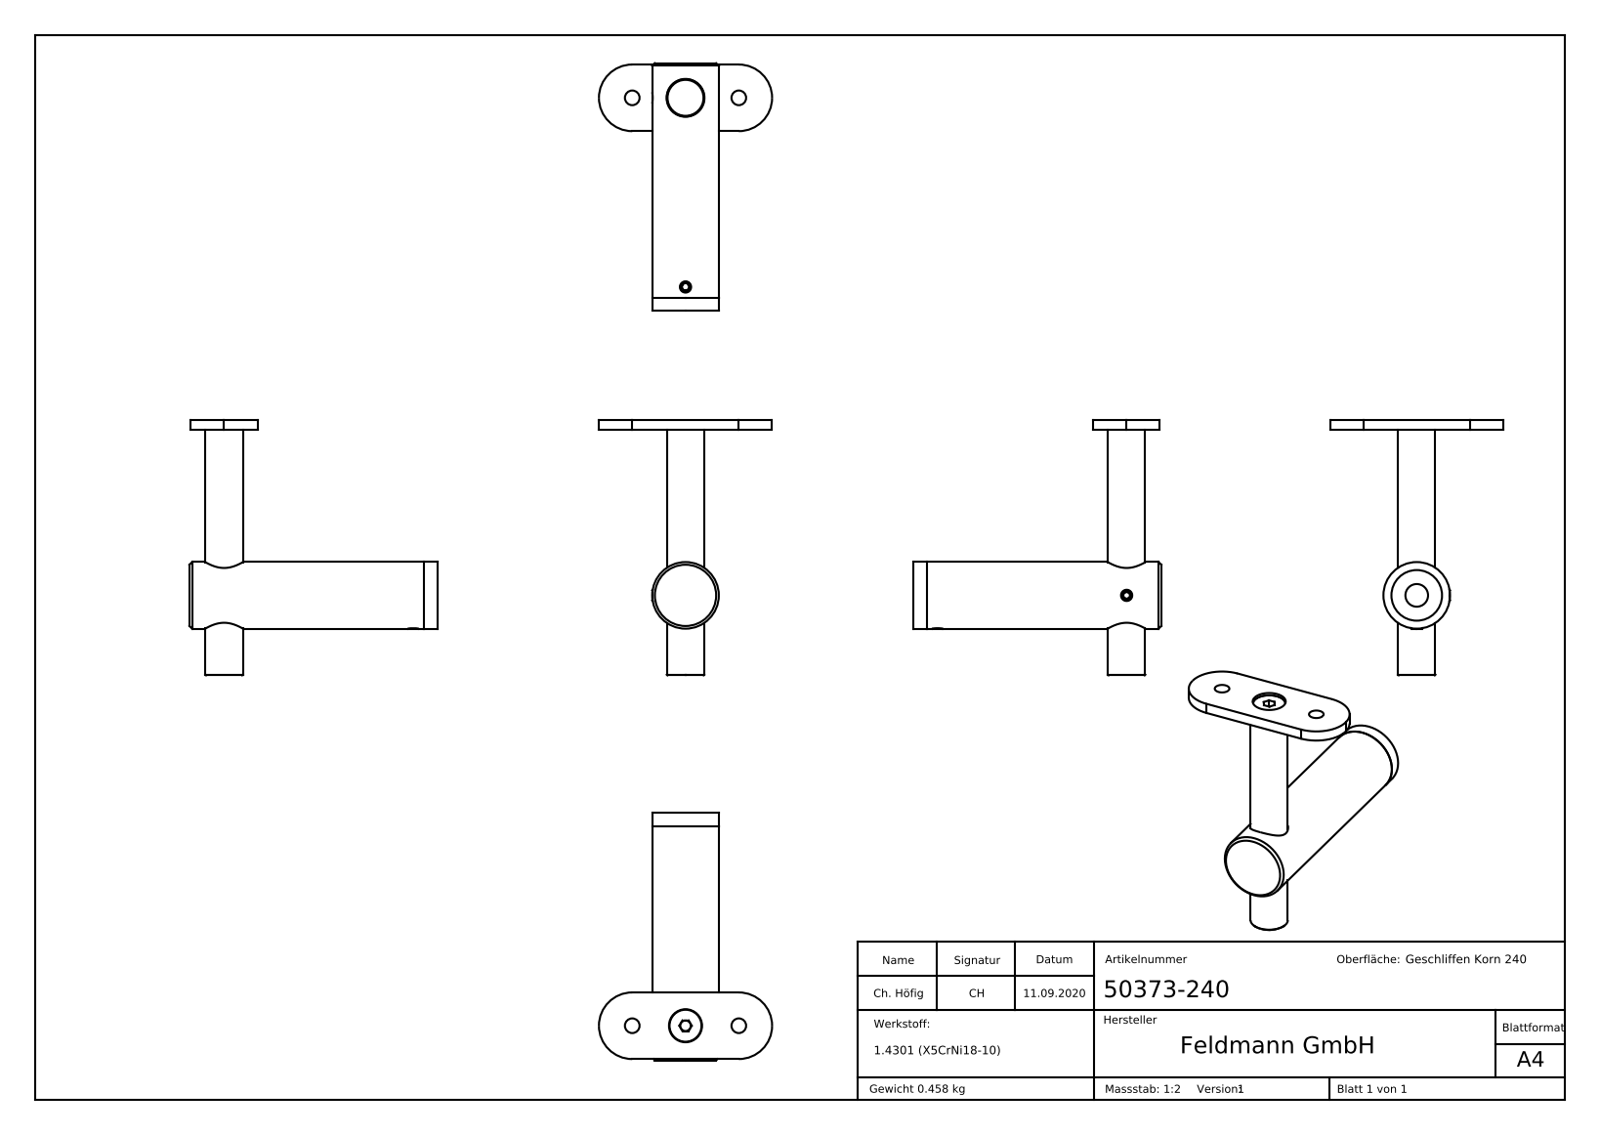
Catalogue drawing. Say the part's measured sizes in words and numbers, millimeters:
The part is named "50373-240; DIN913_DIN 913 M5x5; 5037X-240 Teil3; DIN-7991 M3-M10_DIN7991 M6x14 (+8 more)". Its 3-D file was written by "SolidWorks 2018 (CONFIG_CONTROL_DESIGN)". It is 7 solids with 358 faces: 145 planar, 69 cylindrical and 144 other. Overall it measures 96 by 93 by 88 millimeters. Its volume is 58 036 cubic millimeters and its surface area 21 306 square millimeters. Round holes: 2 of diameter 4.2, 2 of diameter 5.5, 1 of diameter 5, 1 of diameter 8, 1 of diameter 8.5, 1 of diameter 12.4, 1 of diameter 14, 1 of diameter 14.2, 1 of diameter 16, 1 of diameter 19. Round bosses or shafts: 2 of diameter 5, 1 of diameter 25, 1 of diameter 12, 1 of diameter 6. Partial cylindrical surfaces (rounded edges, fillets, slot ends): 2 of radius 12.5, 1 of radius 8.1. The main face-to-face distances are 4, 88, 92.5, 0.5, 3, 91, 5, 2, 93, 62.5. The hole center spacings are 20, 73.76, 40, 71.
